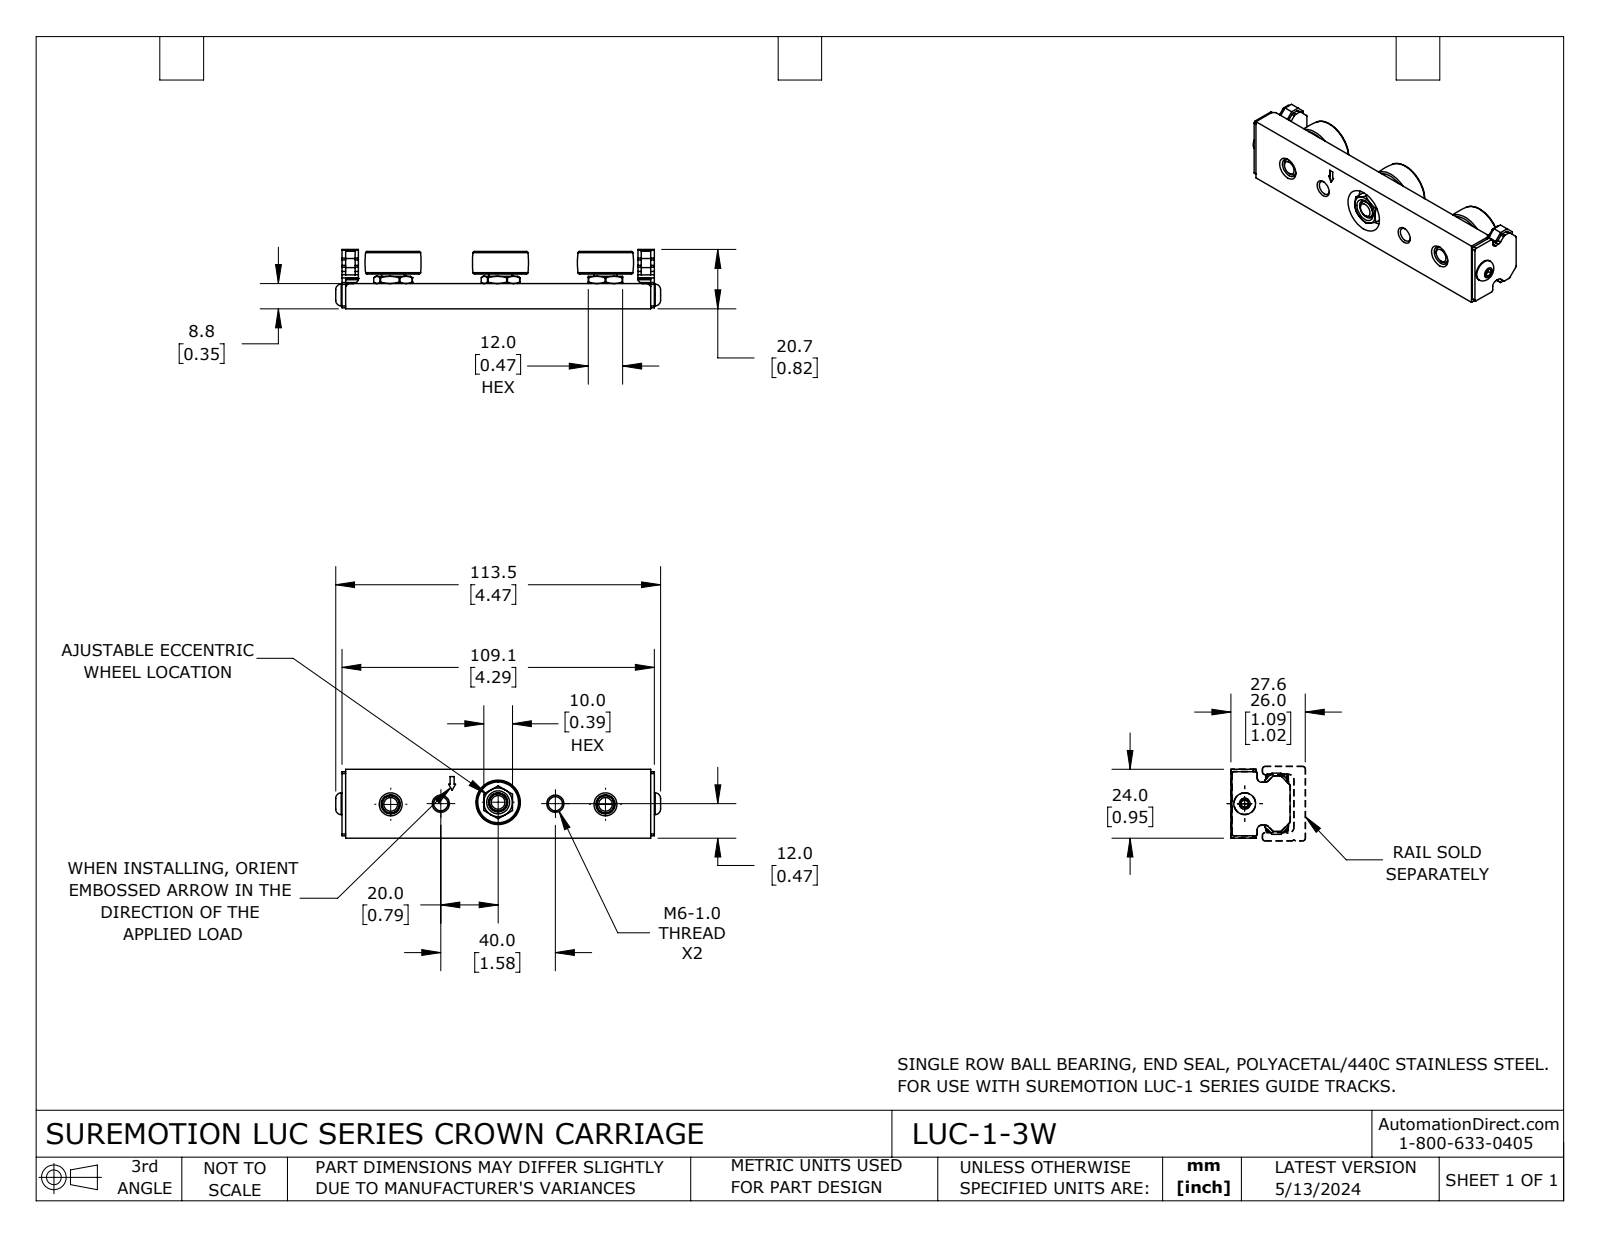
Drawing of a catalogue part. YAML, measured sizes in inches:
part_name: "LUC-1-3W"
step_written_by: "SolidWorks 2023 (CONFIG_CONTROL_DESIGN)"
units: inches
bodies: {solids: 7, faces: 480, planar: 193, cylindrical: 148, other: 139}
overall_size: [4.467, 0.945, 0.816]
volume: 1.924
surface_area: 24.92
round_holes:
  - {diameter: 0.262, count: 3}
  - {diameter: 0.472, count: 3}
  - {diameter: 0.128, count: 1}
  - {diameter: 0.194, count: 1}
  - {diameter: 0.194, count: 1}
  - {diameter: 0.25, count: 1}
  - {diameter: 0.61, count: 1}
round_bosses_or_shafts:
  - {diameter: 0.315, count: 3}
  - {diameter: 0.248, count: 3}
  - {diameter: 0.236, count: 3}
  - {diameter: 0.173, count: 3}
  - {diameter: 0.561, count: 1}
  - {diameter: 0.299, count: 1}
  - {diameter: 0.157, count: 1}
partial_cylinders:
  - {radius: 0.015, count: 12}
  - {radius: 0.033, count: 6}
  - {radius: 0.025, count: 4}
  - {radius: 0.063, count: 4}
  - {radius: 0.269, count: 3}
  - {radius: 0.07, count: 2}
face_to_face_distances: [0.347, 0.945, 0.05, 4.244, 0.052, 0.258, 0.132, 0.479, 0.31, 0.442]
hole_center_spacings: [2.264, 0.689, 2.92, 2.953, 0.033, 0.033, 0.033, 0.656]
